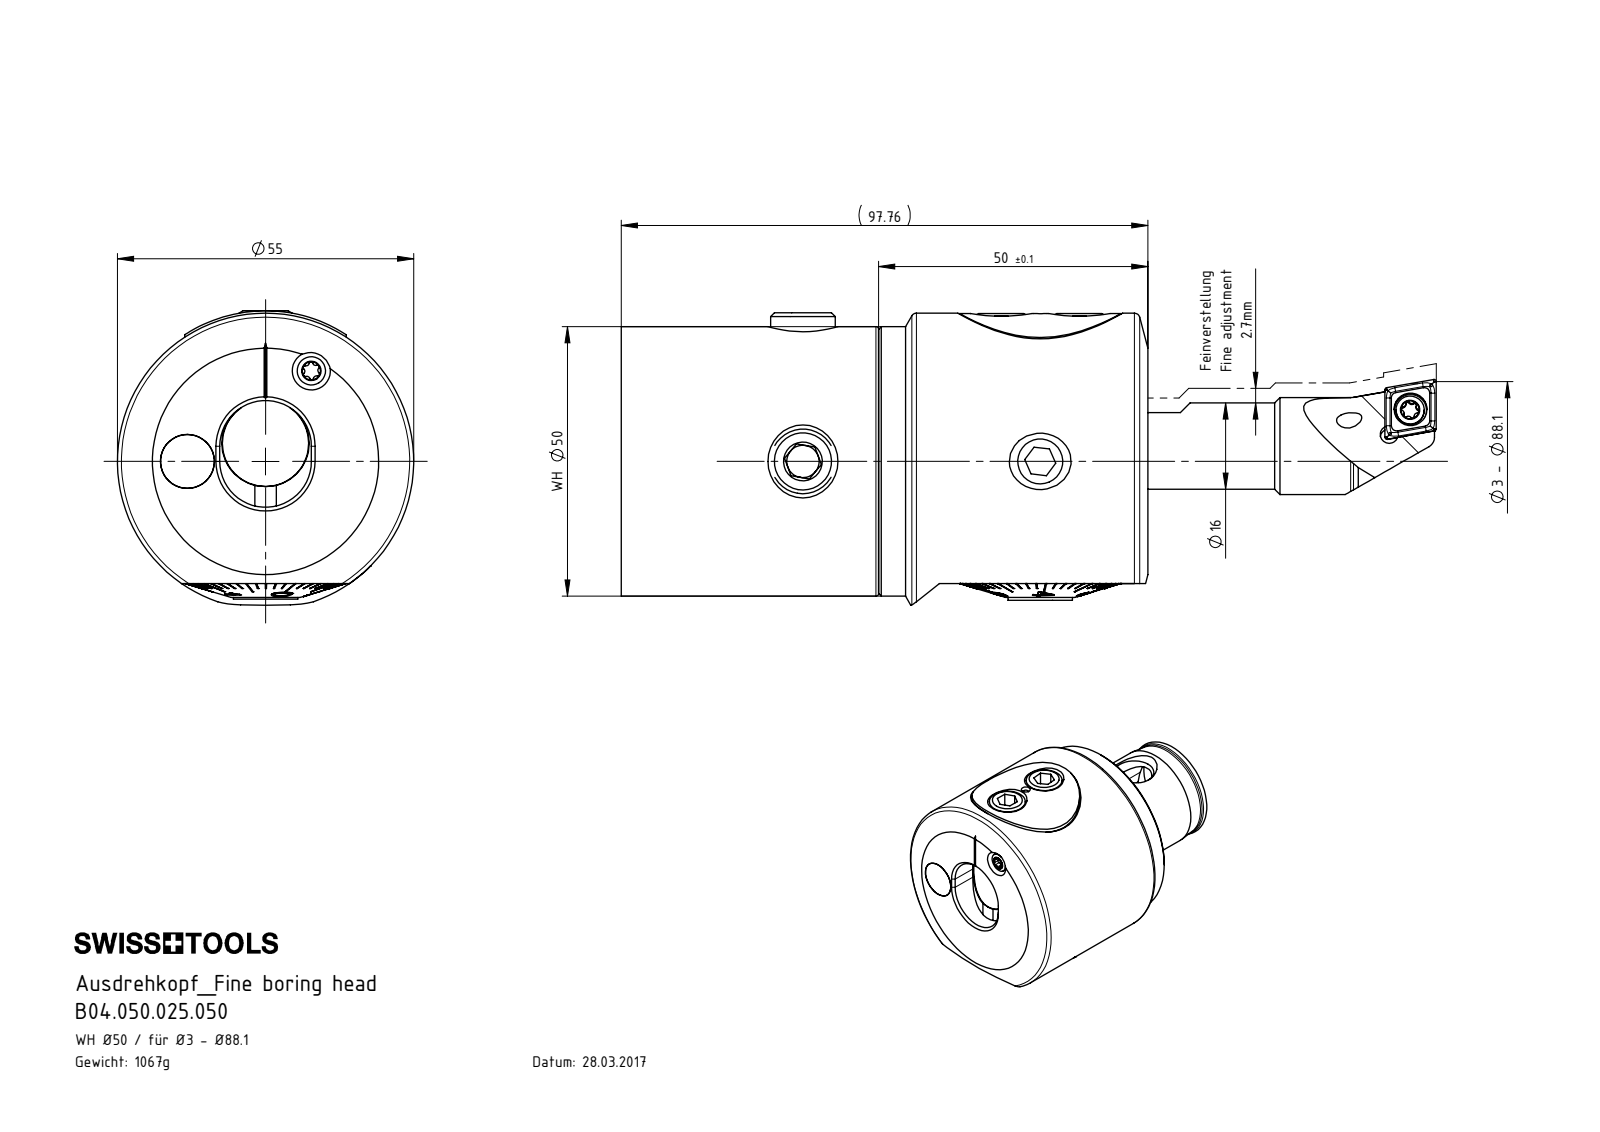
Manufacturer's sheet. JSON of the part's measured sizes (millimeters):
{"part_name": "A55-BG2.012.006_B; ISO 4026 - M10 x 16_PreviewCfg; A55-BG1.011.041_E; B25-WCB.K11.115 (+8 more)", "step_written_by": "SolidWorks 2017 (CONFIG_CONTROL_DESIGN)", "units": "millimeters", "bodies": {"solids": 20, "faces": 920, "planar": 372, "cylindrical": 178, "other": 370}, "overall_size": [151.26, 55, 54.24], "volume_mm3": 199572, "surface_area_mm2": 60754, "round_holes": [[8.5, 4], [3.3, 3], [3, 2], [6, 2], [11, 2], [1, 1], [1.6, 1], [2, 1], [4.2, 1], [4.4, 1], [6.1, 1], [8, 1]], "round_bosses_or_shafts": [[12, 3], [10, 3], [18, 2], [5.25, 2], [4, 2], [55, 1], [50, 1], [29.9, 1]], "partial_cylinders_radius": [[0.34, 12], [0.59, 12], [3.2, 3], [8.5, 2], [0.5, 1], [2, 1], [3.5, 1], [9.2, 1]], "face_to_face_distances": [47.76, 97.76, 50, 6, 1.5, 19.26, 28.5, 78.5, 8.19, 8.49], "hole_center_spacings": [7.25, 14.5, 44.05, 2.84, 6.06, 6.19, 14.78, 16.34]}
